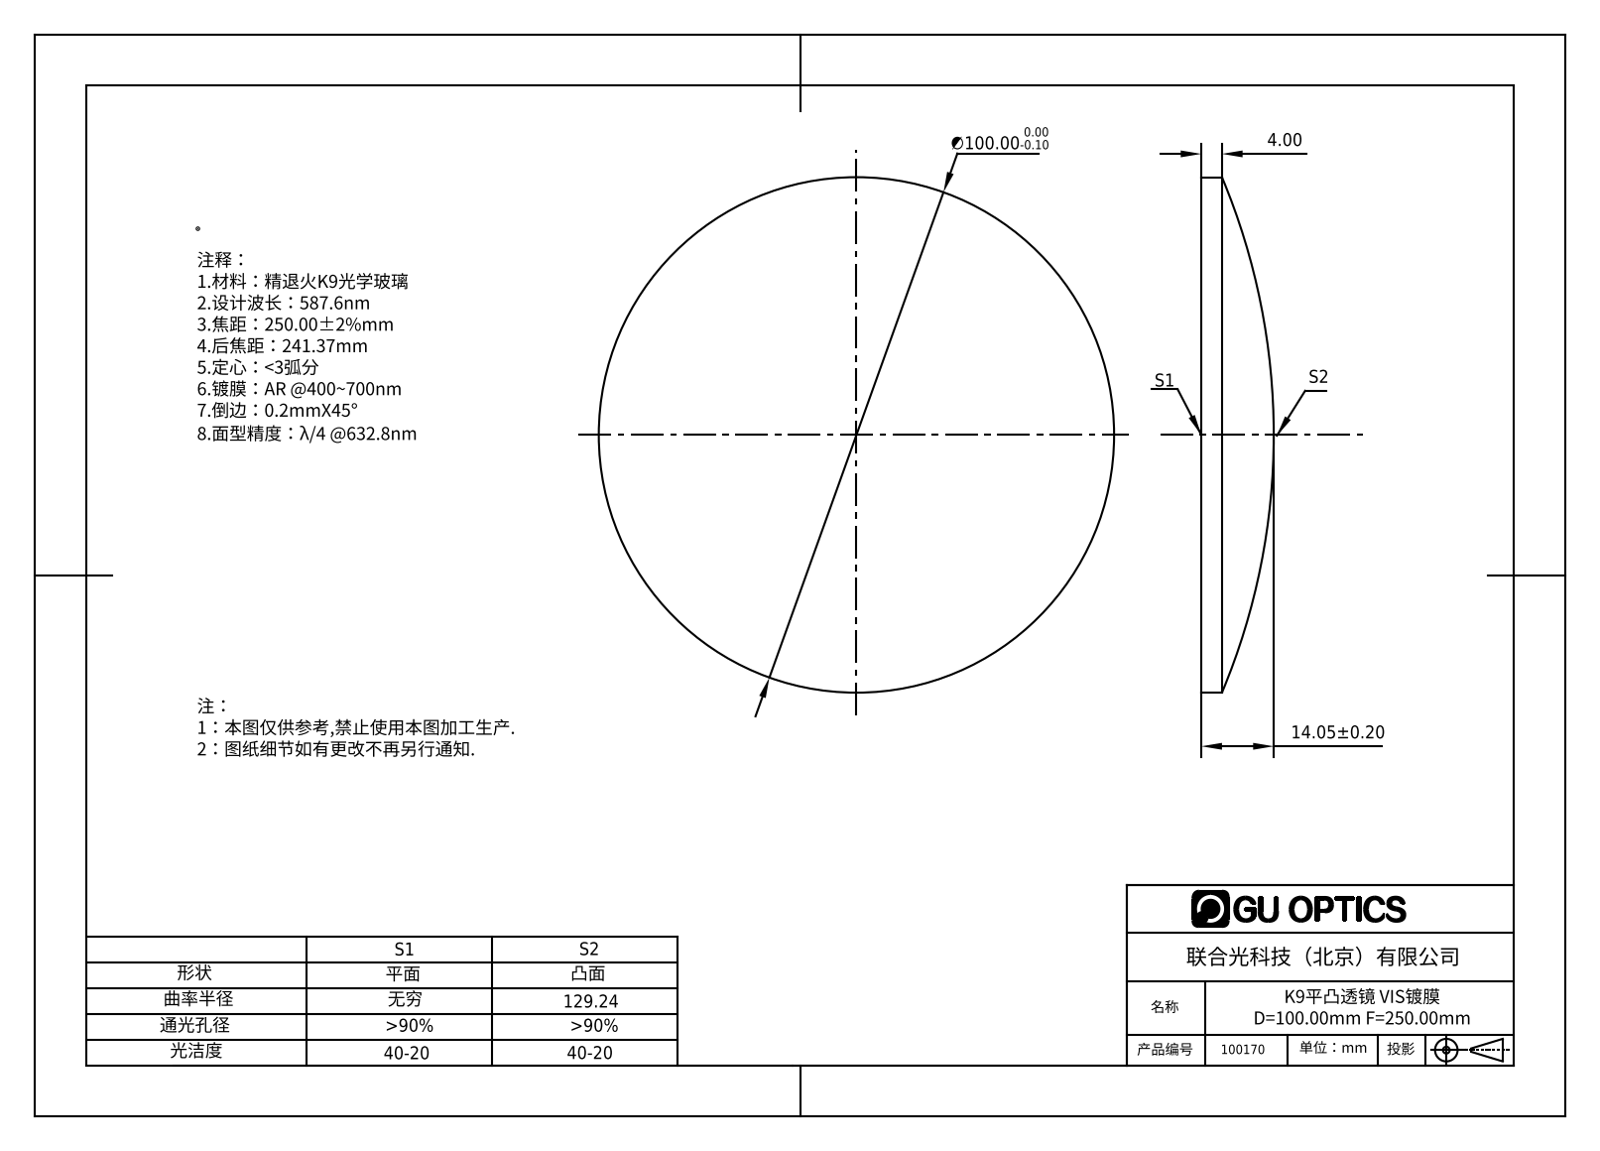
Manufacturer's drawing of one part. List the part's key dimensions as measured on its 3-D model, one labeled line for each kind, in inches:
Part name (STEP PRODUCT): 100170
STEP written by: SolidWorks 2016 (AUTOMOTIVE_DESIGN)
Units: inches
Bodies: 1 solid, 5 faces (1 planar, 2 cylindrical, 2 other)
Overall size (bounding box): 3.937 × 3.937 × 0.553
Volume: 4.358 in³ · Surface area: 26.79 in²
Round bosses / shafts (diameter × count): ⌀3.937 ×1
